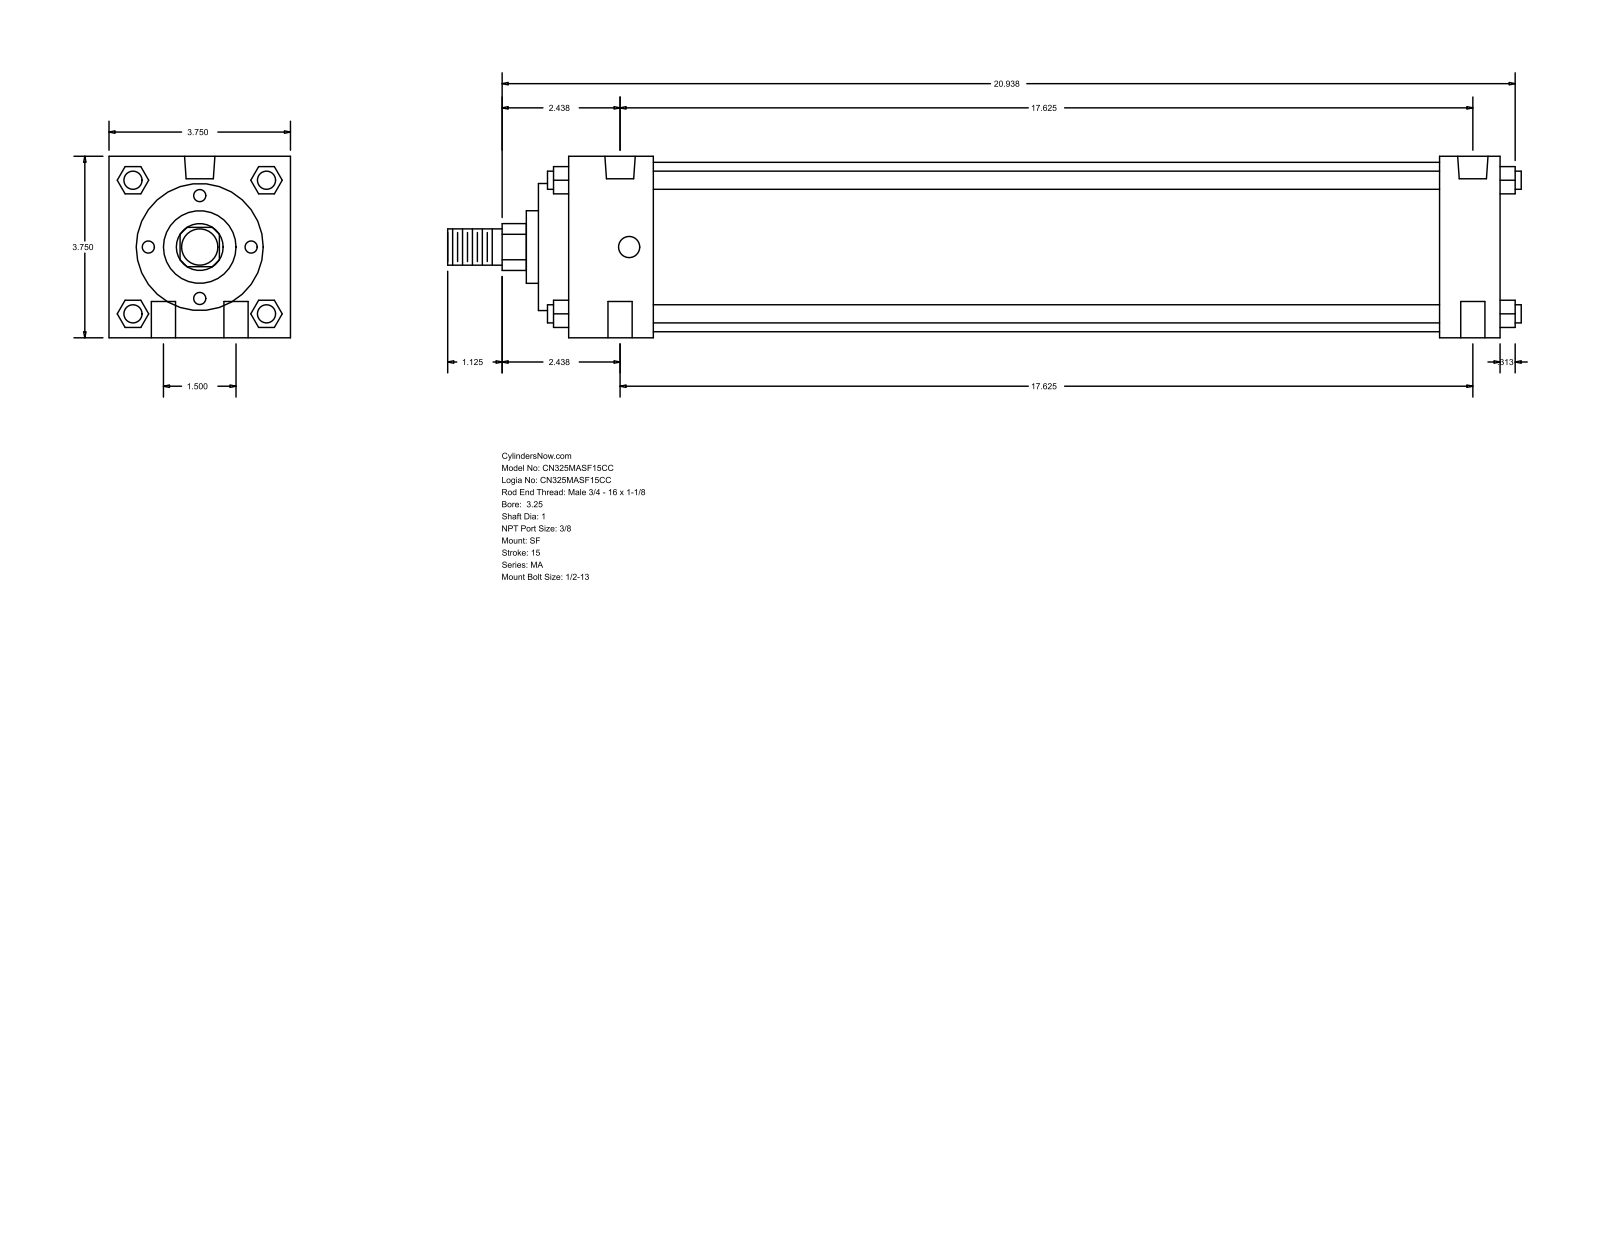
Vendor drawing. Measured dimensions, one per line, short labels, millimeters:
name: MA_SF__0325_1
written by: GSSL Pune (CONFIG_CONTROL_DESIGN)
unit: mm
bodies: 0 solids, 126 faces (95 planar, 31 cylindrical, 0 other)
size: 563.56 × 95.25 × 95.25
holes: 4× ⌀12.7, 2× ⌀11.11, 2× ⌀15.93
bosses: 4× ⌀9.53, 1× ⌀88.9, 1× ⌀66.67, 1× ⌀38.1, 1× ⌀25.4, 1× ⌀19.05
rounds: 1× R12.29
face distances: 95.24, 488.96, 457.2, 31.76, 44.46, 412.74, 444.5, 15.87, 60.33, 473.07
hole spacings: 19.05, 448.09, 447.68, 38.1, 449.3, 438.15
